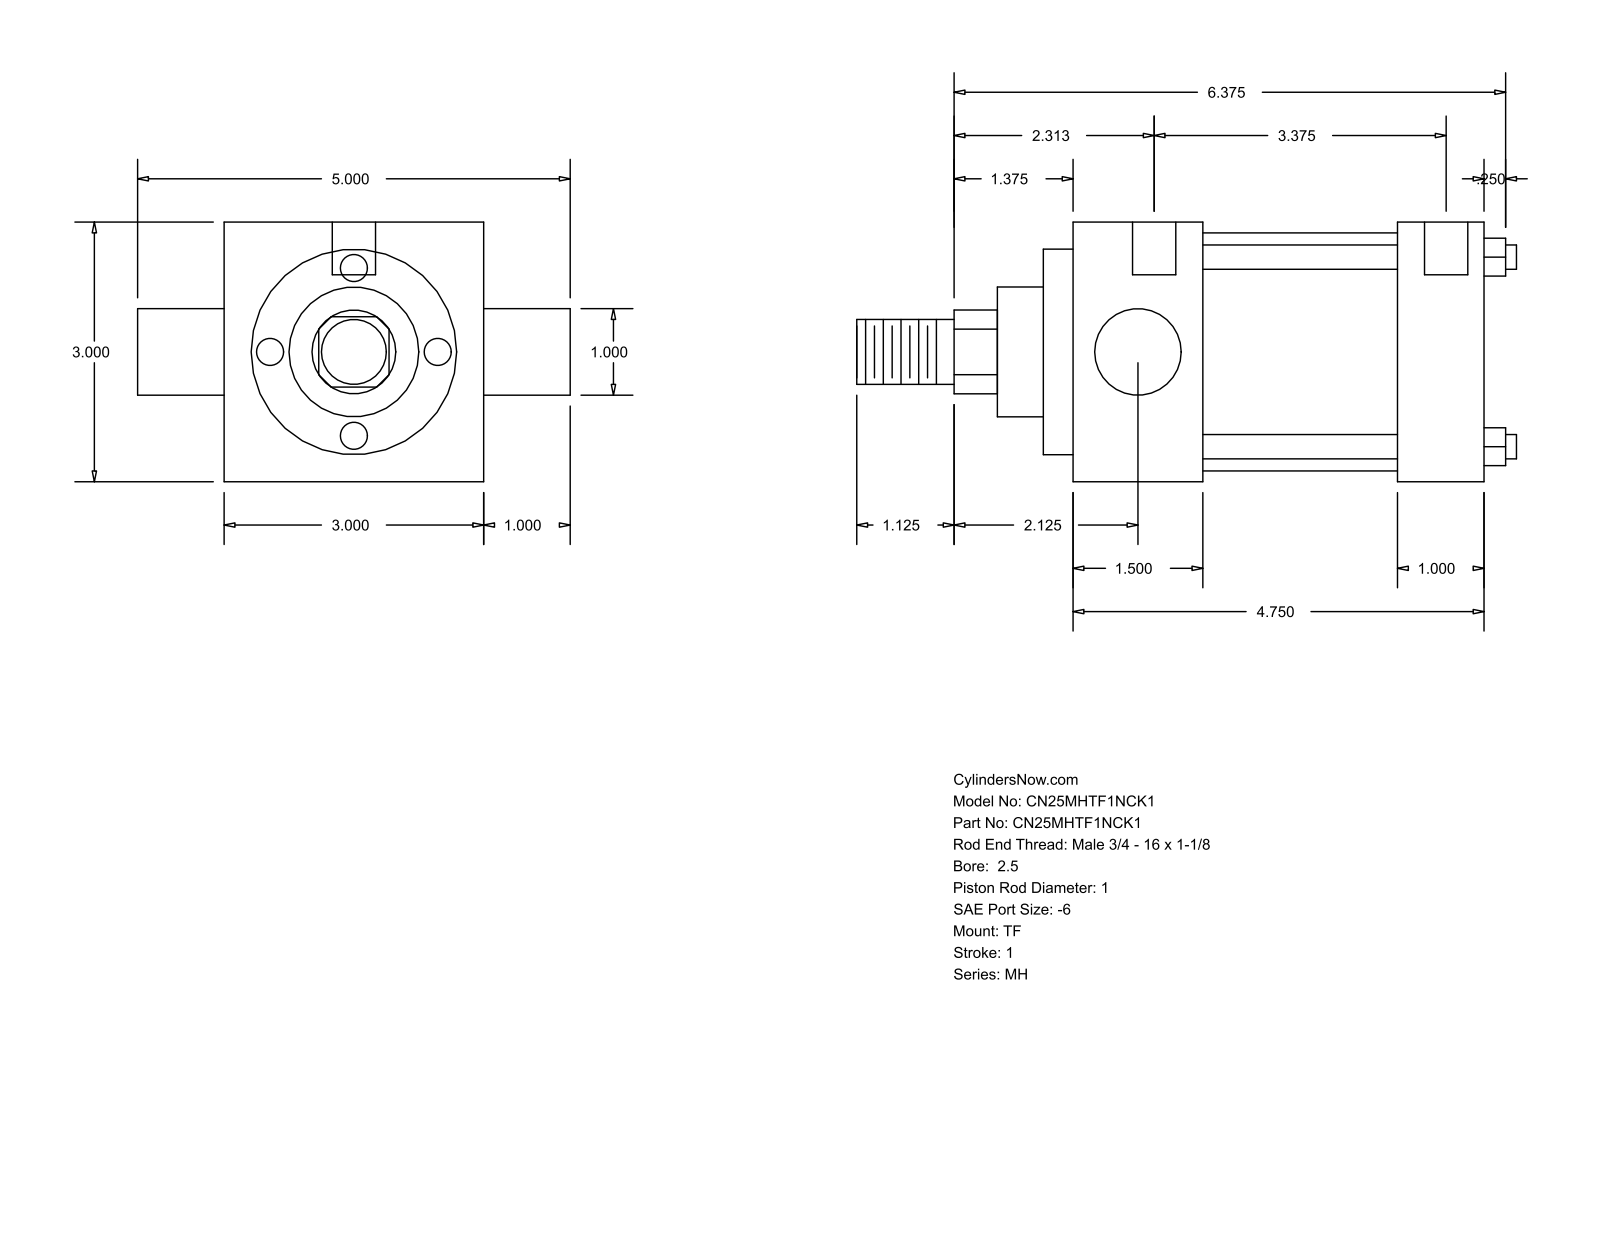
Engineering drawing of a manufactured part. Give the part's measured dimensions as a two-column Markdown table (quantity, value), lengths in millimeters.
| quantity | value |
| --- | --- |
| part name | MH_TF__0250_1 |
| STEP written by | GSSL Pune (CONFIG_CONTROL_DESIGN) |
| units | millimeters |
| bodies | 0 solids, 86 faces (61 planar, 25 cylindrical, 0 other) |
| overall size | 193.68 × 127 × 76.2 |
| round holes (diameter × count) | 5.56 × 3, 12.7 × 2 |
| round bosses / shafts (diameter × count) | 7.14 × 4, 25.4 × 2, 69.85 × 1, 60.33 × 1, 38.1 × 1, 19.05 × 1 |
| partial cylindrical surfaces (radius × count) | 12.29 × 1 |
| main face-to-face distances | 76.2, 120.65, 25.39, 38.11, 82.54, 95.26, 57.15, 8.73, 46.84, 103.99 |
| hole center spacings | 3.18, 4.76, 85.72, 88.9, 90.48, 93.66 |
